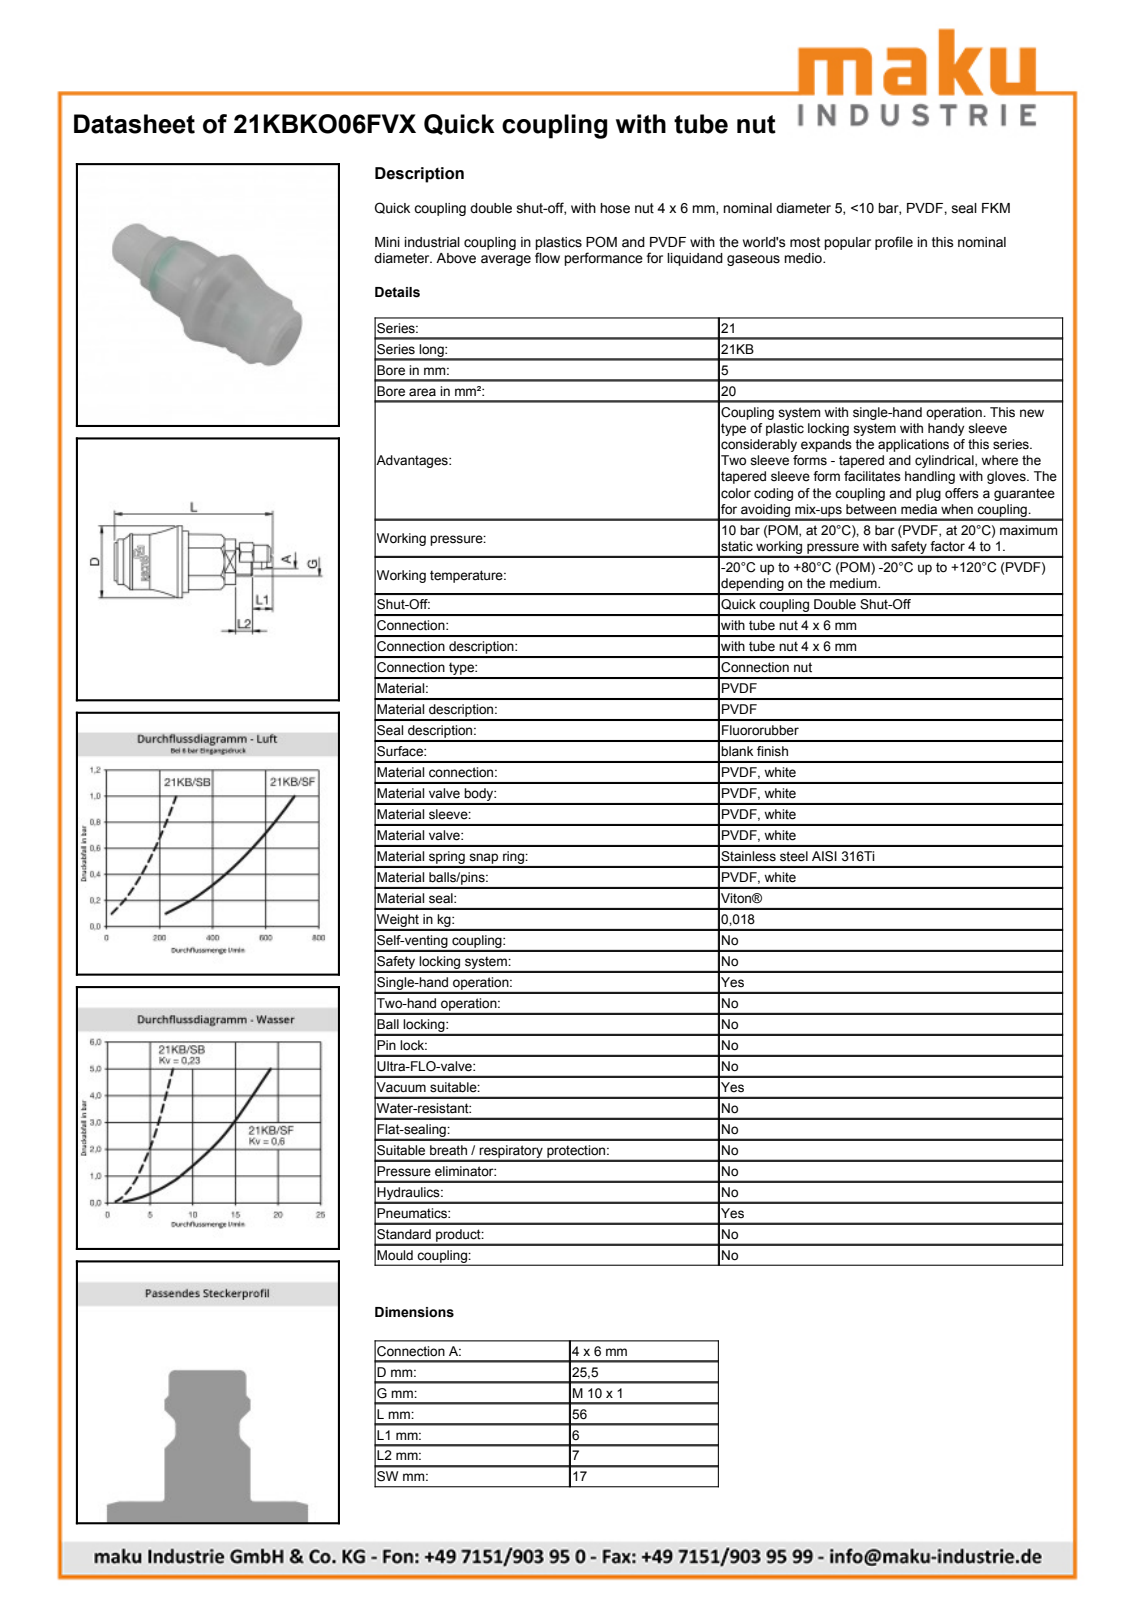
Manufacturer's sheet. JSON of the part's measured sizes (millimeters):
{"part_name": "D115072", "step_written_by": "Autodesk Inventor 2013 (AUTOMOTIVE_DESIGN)", "units": "millimeters", "bodies": {"solids": 1, "faces": 319, "planar": 162, "cylindrical": 87, "other": 70}, "overall_size": [55.9, 25.3, 25.3], "volume_mm3": 11356, "surface_area_mm2": 7977, "round_holes": [[6.2, 1], [8, 1], [8.92, 1], [12.2, 1], [13.15, 1], [13.5, 1], [16.3, 1], [22, 1]], "round_bosses_or_shafts": [[25.3, 1], [21.9, 1], [19.65, 1], [19.3, 1], [15.8, 1], [14.15, 1], [13.35, 1], [12.11, 1]], "partial_cylinders_radius": [[4.69, 18], [6, 1], [6.93, 1], [8, 1], [9.85, 1]], "face_to_face_distances": [16.8, 26, 42.8, 12, 18.95, 2.15, 23.85, 4, 12.8, 14.95]}
